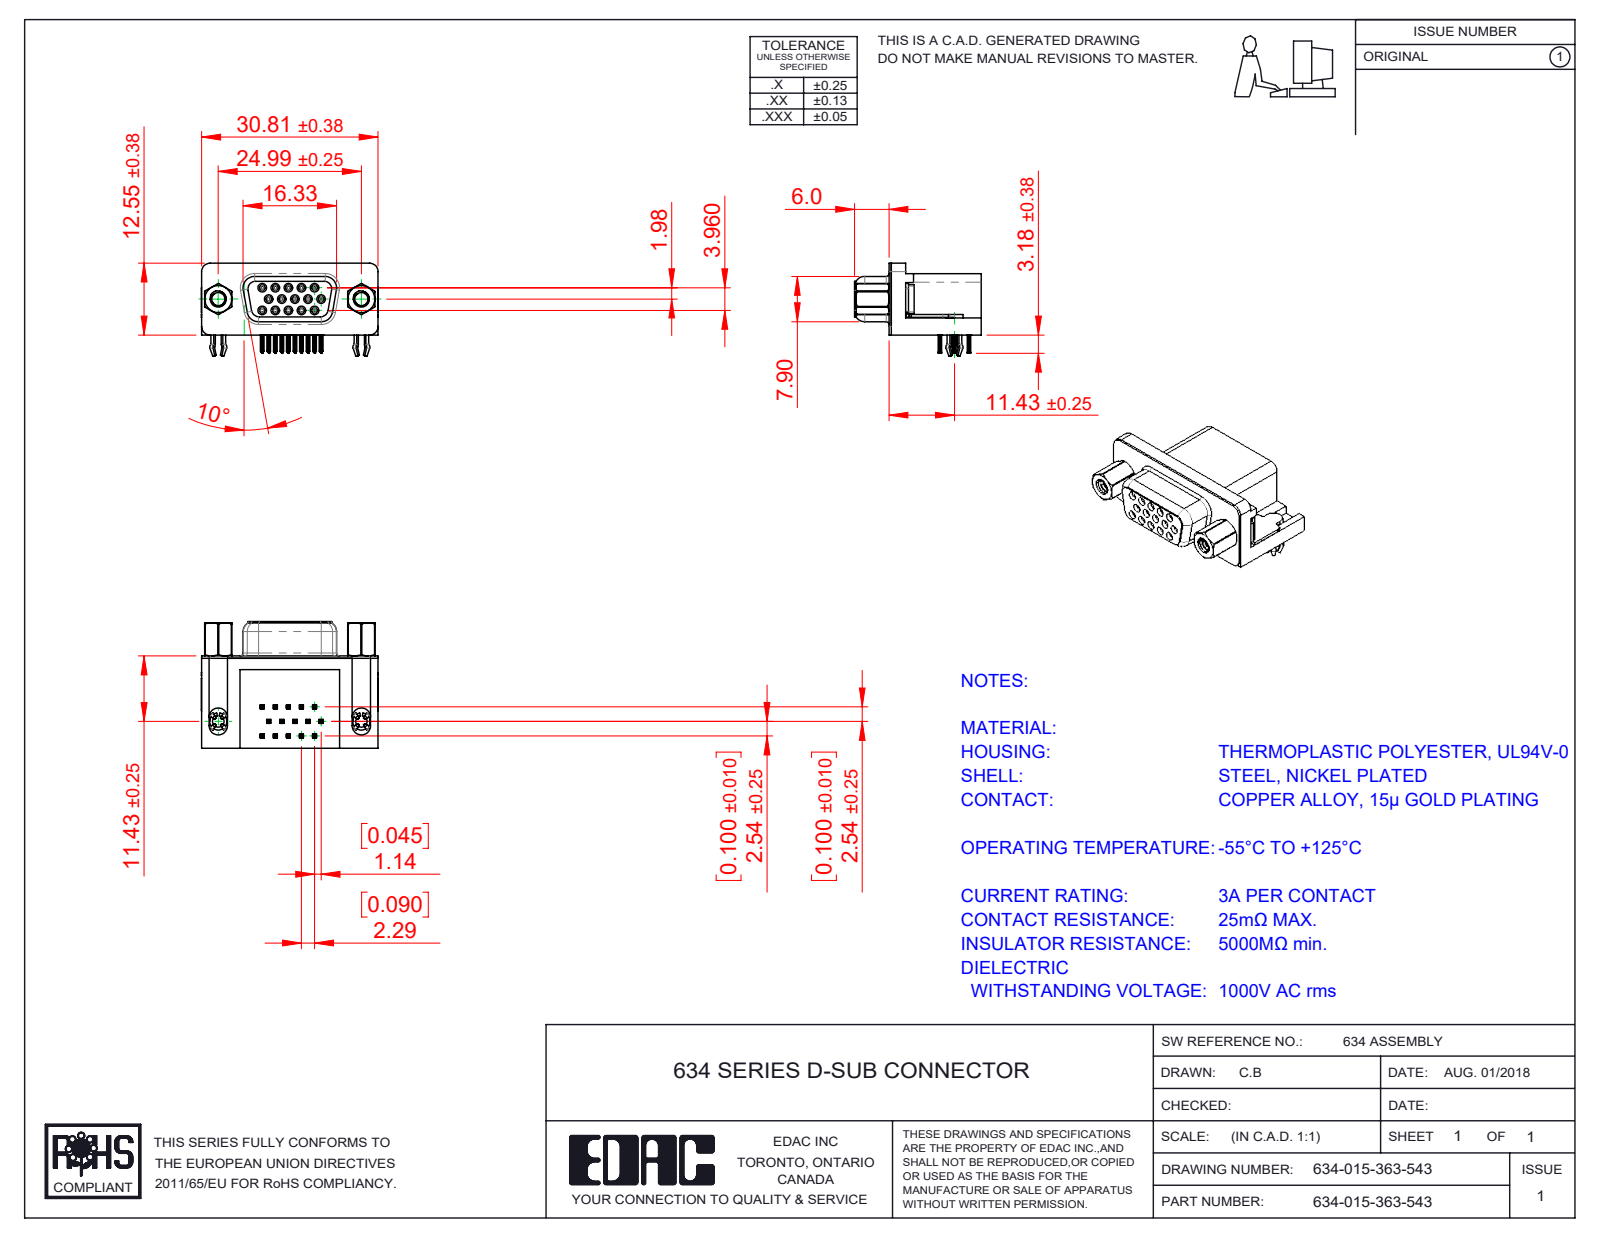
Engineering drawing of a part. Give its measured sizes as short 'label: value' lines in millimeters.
name: 4 Prong Board Lock; Contact Bottom; 4-40 Hex Standoff; Contact Top (+5 more)
written by: SolidWorks 2016 (CONFIG_CONTROL_DESIGN)
unit: mm
bodies: 23 solids, 2661 faces (1130 planar, 669 cylindrical, 862 other)
size: 30.89 × 22.1 × 16.25
volume: 4 765 mm³; area: 7 029 mm²
holes: 15× ⌀0.8, 15× ⌀0.9, 2× ⌀2, 2× ⌀2.26, 2× ⌀2.29, 2× ⌀4, 2× ⌀4.8, 2× ⌀5
bosses: 15× ⌀1.2, 2× ⌀4.9, 2× ⌀4.75, 2× ⌀3.9, 2× ⌀3, 2× ⌀2.79
rounds: 120× R0.1, 60× R0.15, 30× R0.35, 19× R1, 15× R0.34, 12× R0.25, 8× R1.35, 8× R1.6
face distances: 0.4, 10.35, 15.7, 16.1, 0.35, 2.5, 2.9, 6.4, 0.6, 10.7
hole spacings: 2.29, 2.28, 3.96, 4.57, 6.05, 3.97, 4.58, 6.86
